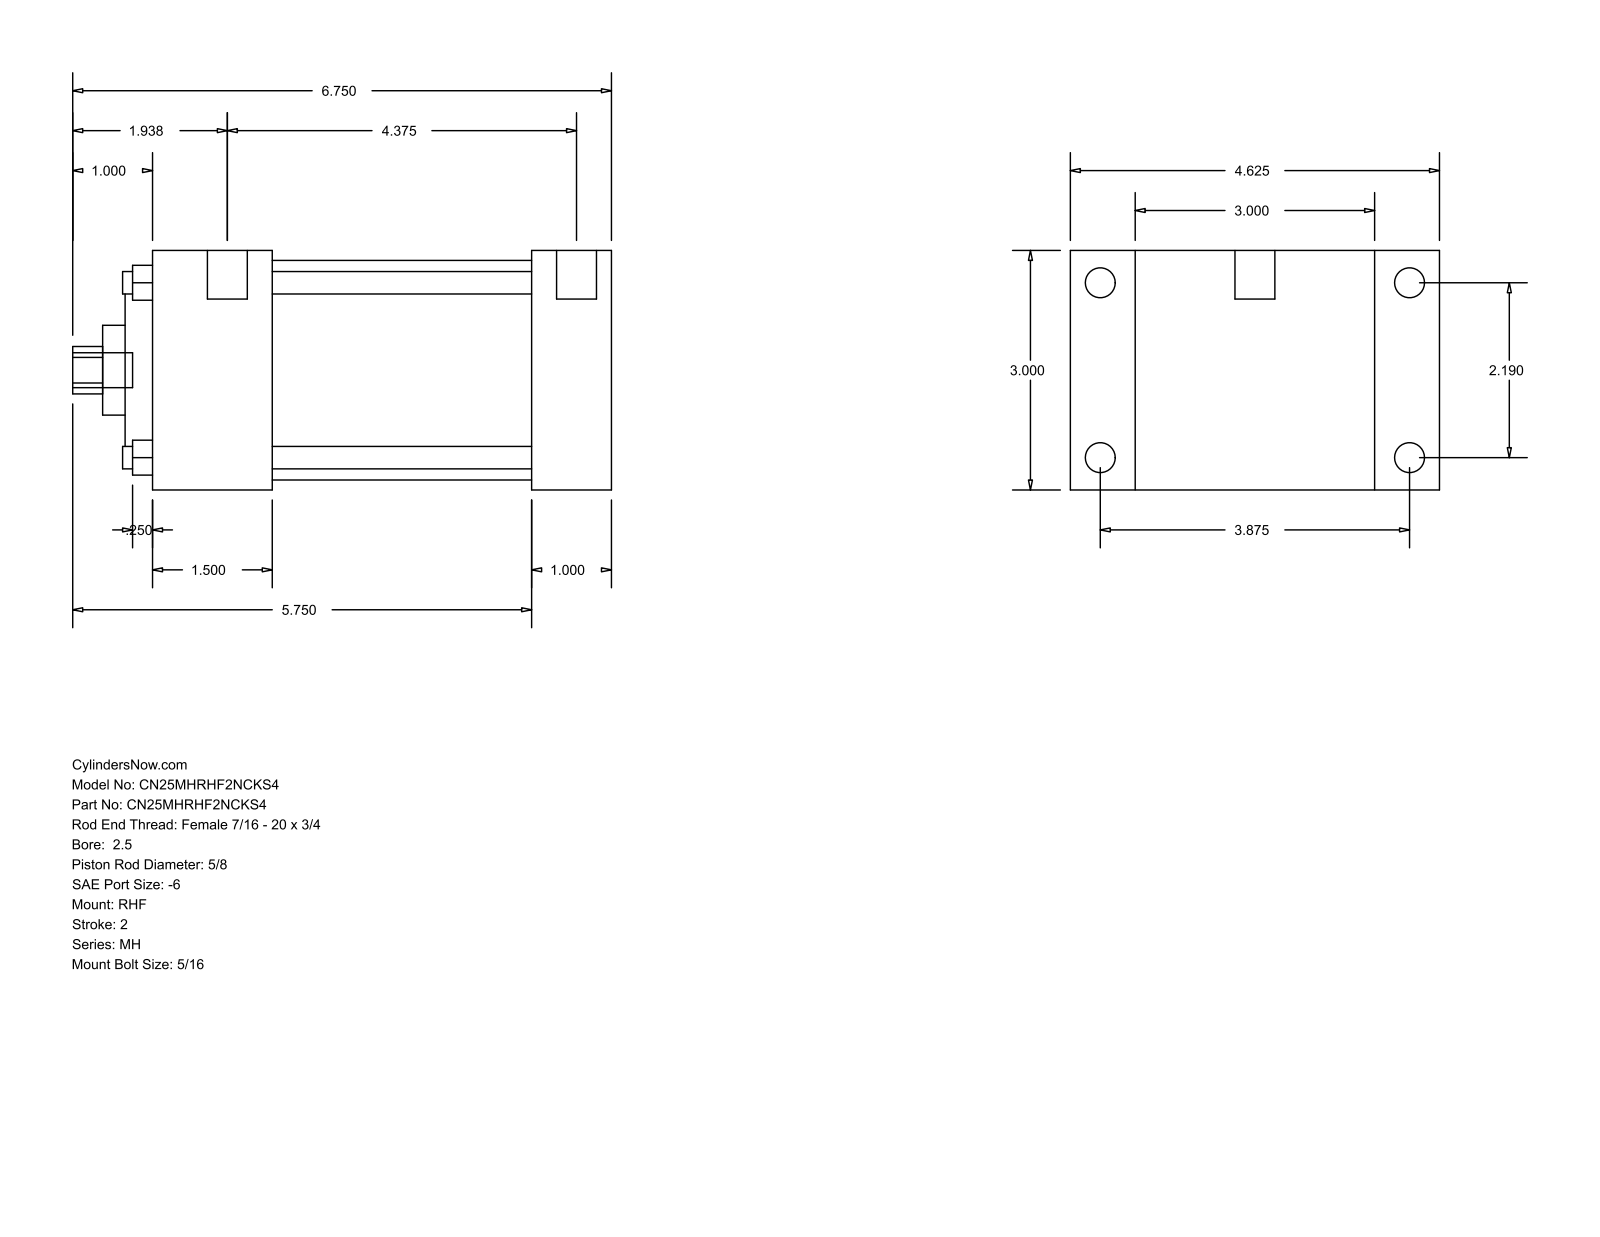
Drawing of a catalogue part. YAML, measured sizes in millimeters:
part_name: "MH_RHF__0250_0.625"
step_written_by: "GSSL Pune (CONFIG_CONTROL_DESIGN)"
units: millimeters
bodies: {solids: 0, faces: 90, planar: 61, cylindrical: 29, other: 0}
overall_size: [171.45, 117.47, 76.2]
round_holes:
  - {diameter: 7.14, count: 4}
  - {diameter: 15.88, count: 1}
  - {diameter: 28.57, count: 1}
  - {diameter: 55.55, count: 1}
  - {diameter: 69.85, count: 1}
round_bosses_or_shafts:
  - {diameter: 9.53, count: 4}
  - {diameter: 5.56, count: 4}
  - {diameter: 12.7, count: 2}
  - {diameter: 11.11, count: 1}
partial_cylinders:
  - {radius: 7.54, count: 1}
face_to_face_distances: [76.2, 25.4, 20.64, 96.84, 146.05, 120.65, 117.48, 38.1, 82.55, 107.95]
hole_center_spacings: [39.33, 55.62, 78.66]
